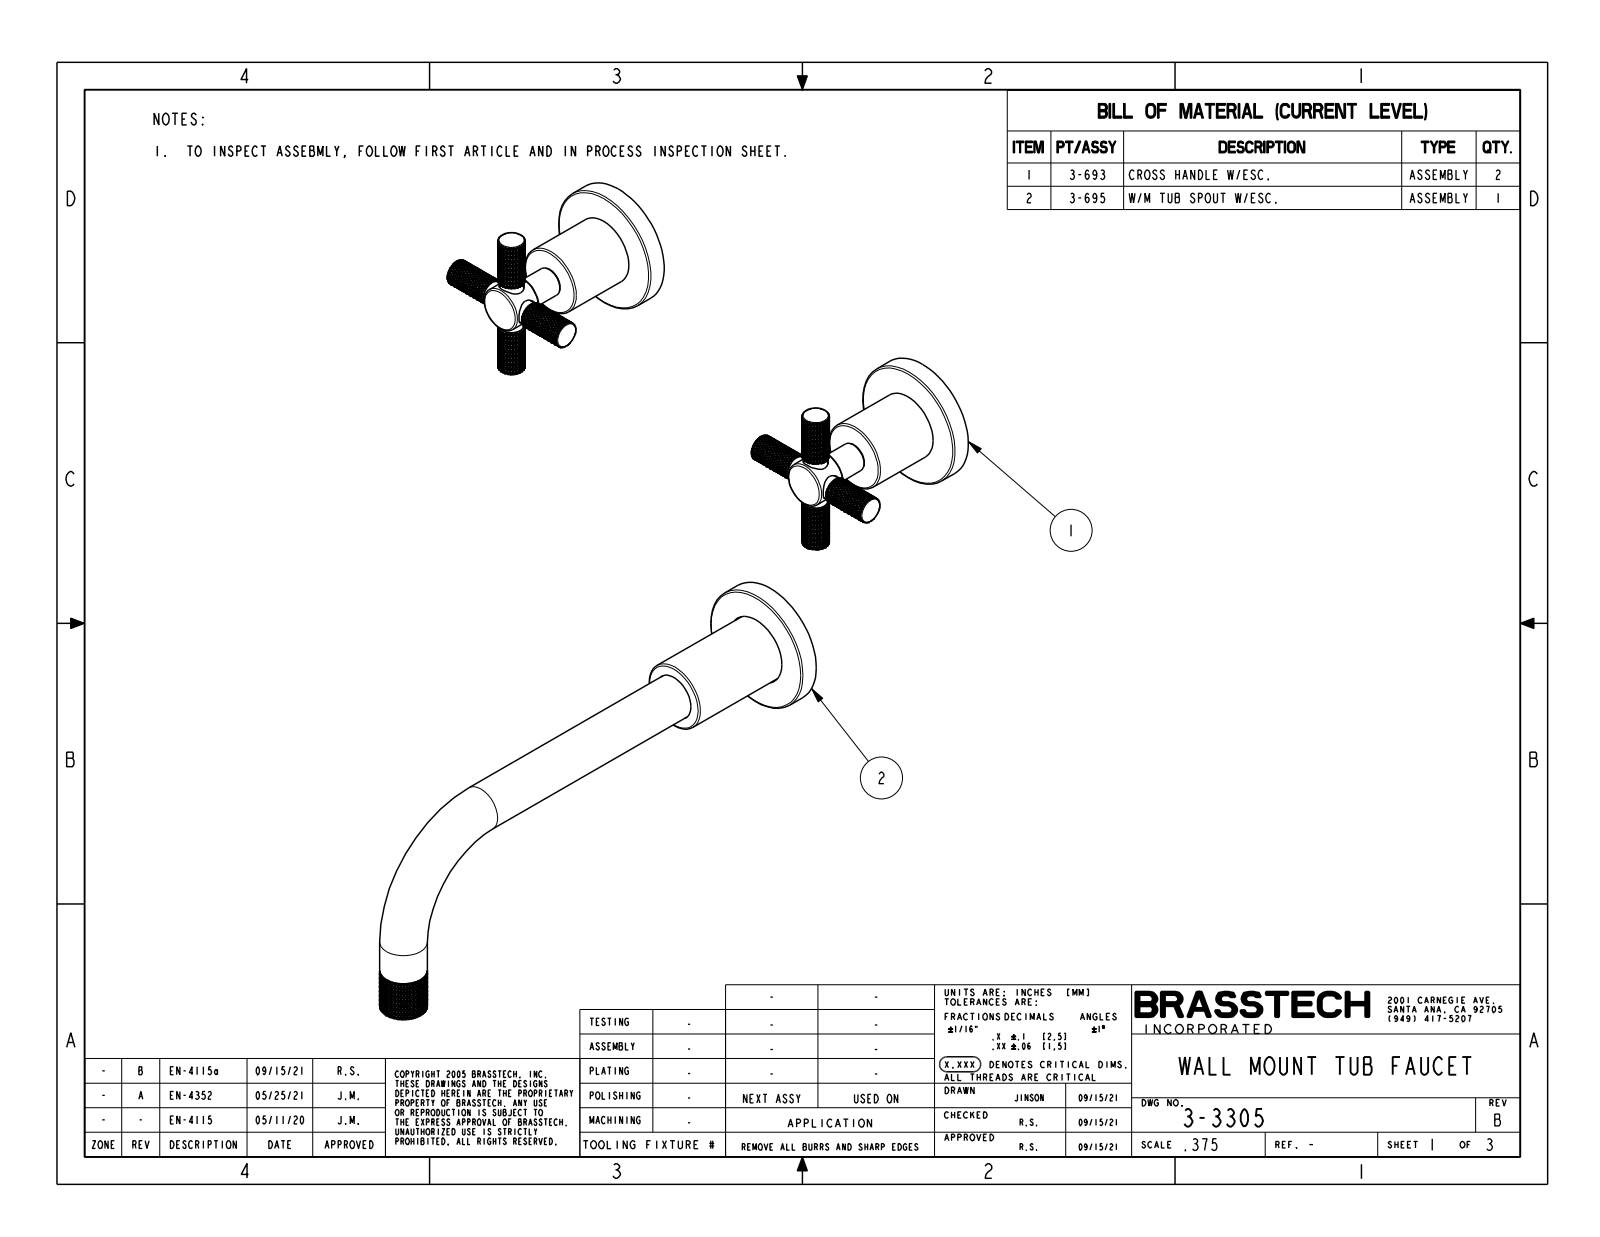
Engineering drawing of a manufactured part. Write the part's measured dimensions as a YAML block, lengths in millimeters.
part_name: "3-3305"
step_written_by: "CREO PARAMETRIC BY PTC INC, 2018400 (CONFIG_CONTROL_DESIGN)"
units: millimeters
bodies: {solids: 3, faces: 26885, planar: 192, cylindrical: 5185, other: 21508}
overall_size: [301.4, 272.4, 252.4]
volume: 325800
surface_area: 71680
round_holes:
  - {diameter: 11.8, count: 3}
  - {diameter: 3, count: 1}
  - {diameter: 15.4, count: 1}
  - {diameter: 17.6, count: 1}
round_bosses_or_shafts:
  - {diameter: 60.3, count: 3}
  - {diameter: 12.7, count: 3}
  - {diameter: 11.2, count: 3}
  - {diameter: 33.4, count: 2}
  - {diameter: 31.8, count: 2}
  - {diameter: 22.2, count: 2}
  - {diameter: 21.6, count: 2}
  - {diameter: 14.3, count: 2}
partial_cylinders:
  - {radius: 7.6, count: 1}
face_to_face_distances: [9.5, 45.1, 35.6, 77.9, 68.4, 32.8, 63.5, 54, 18.4, 14.4]
hole_center_spacings: [198.1, 200]
